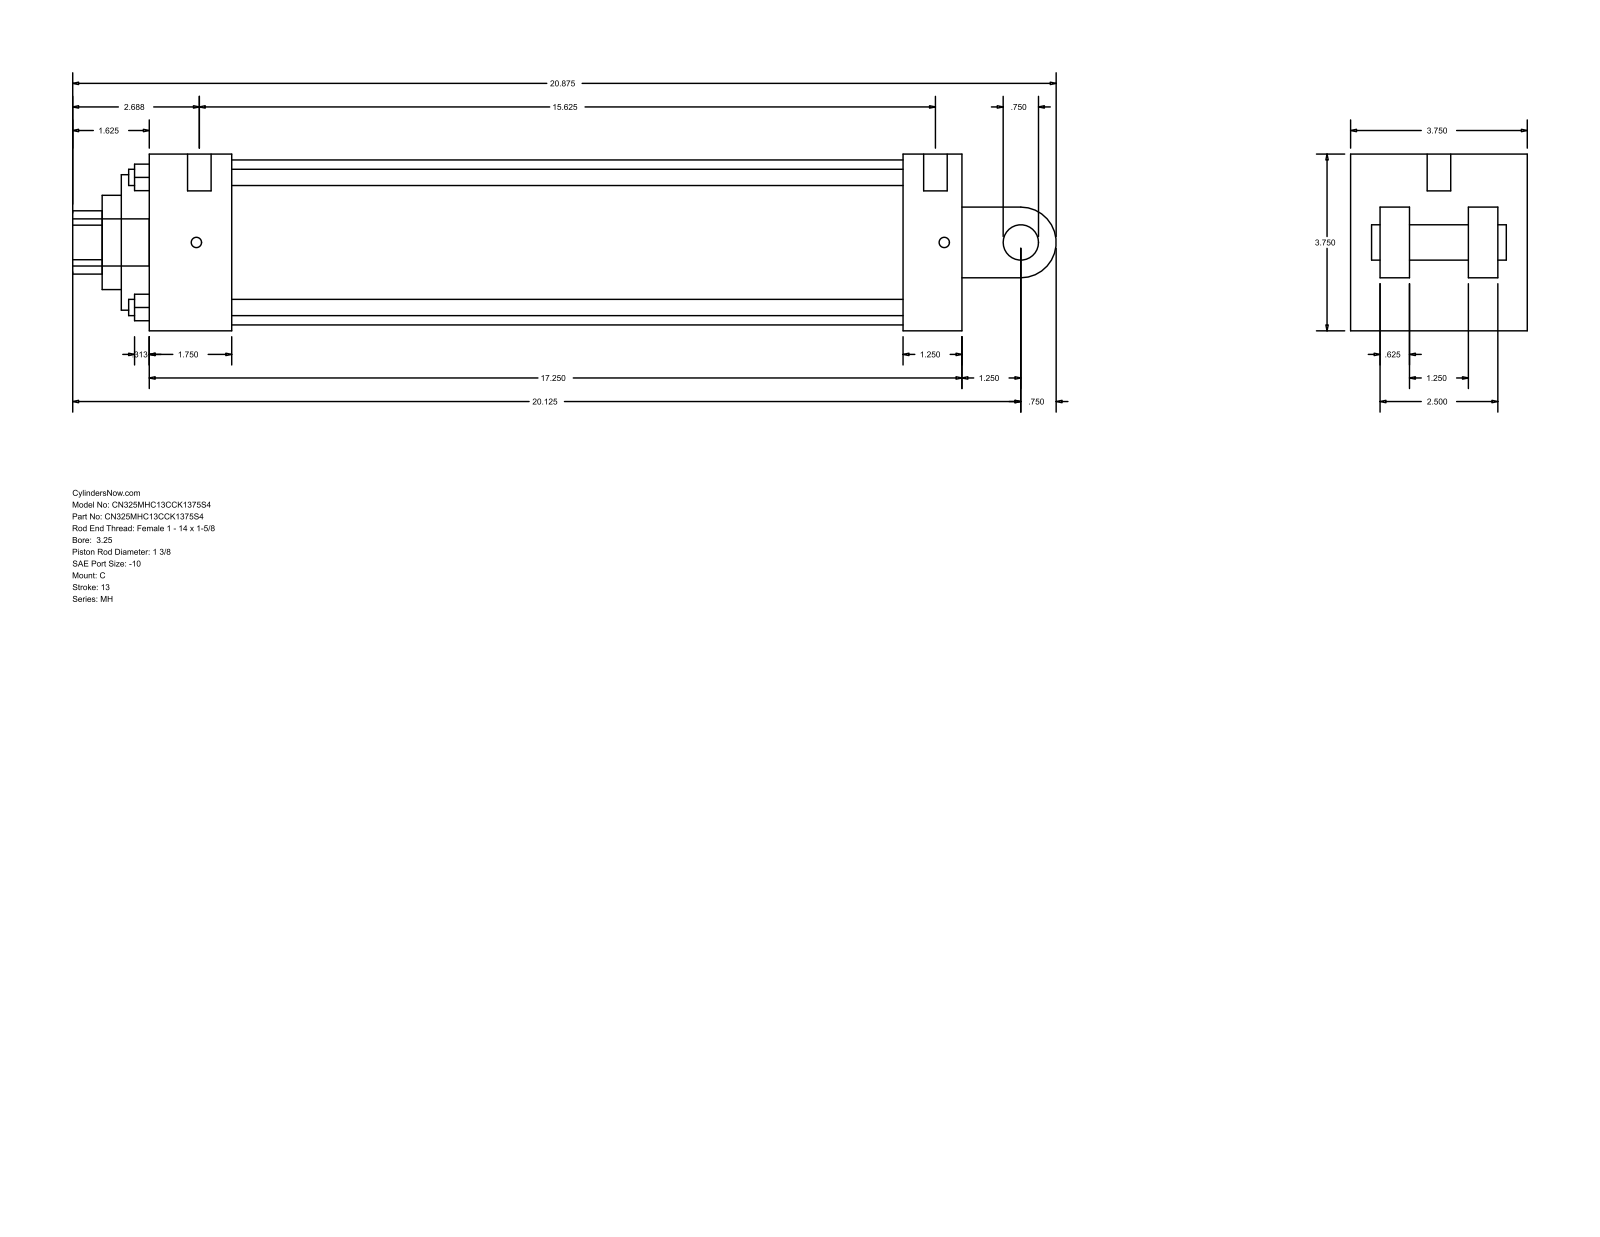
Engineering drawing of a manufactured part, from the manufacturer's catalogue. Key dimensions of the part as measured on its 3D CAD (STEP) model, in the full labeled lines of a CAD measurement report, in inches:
Part name (STEP PRODUCT): MH_C__0325_1.375
STEP written by: GSSL Pune (CONFIG_CONTROL_DESIGN)
Units: inches
Bodies: 0 solids, 101 faces (71 planar, 30 cylindrical, 0 other)
Overall size (bounding box): 20.875 × 3.75 × 3.75
Round holes (diameter × count): ⌀0.345 ×4, ⌀0.219 ×2, ⌀0.5 ×1, ⌀1.375 ×1, ⌀2 ×1, ⌀2.875 ×1, ⌀3.5 ×1
Round bosses / shafts (diameter × count): ⌀0.219 ×2, ⌀1 ×1, ⌀0.75 ×1, ⌀0.5 ×1
Partial cylindrical surfaces — rounded edges, fillets, slot ends (radius × count): R0.672 ×1, R0.75 ×1
Main face-to-face distances: 3.75, 0.625, 17.25, 2.5, 3.125, 1.25, 1.875, 1.75, 16, 14.25
Hole centre spacings: 1.952, 2.76, 3.903, 0.187
